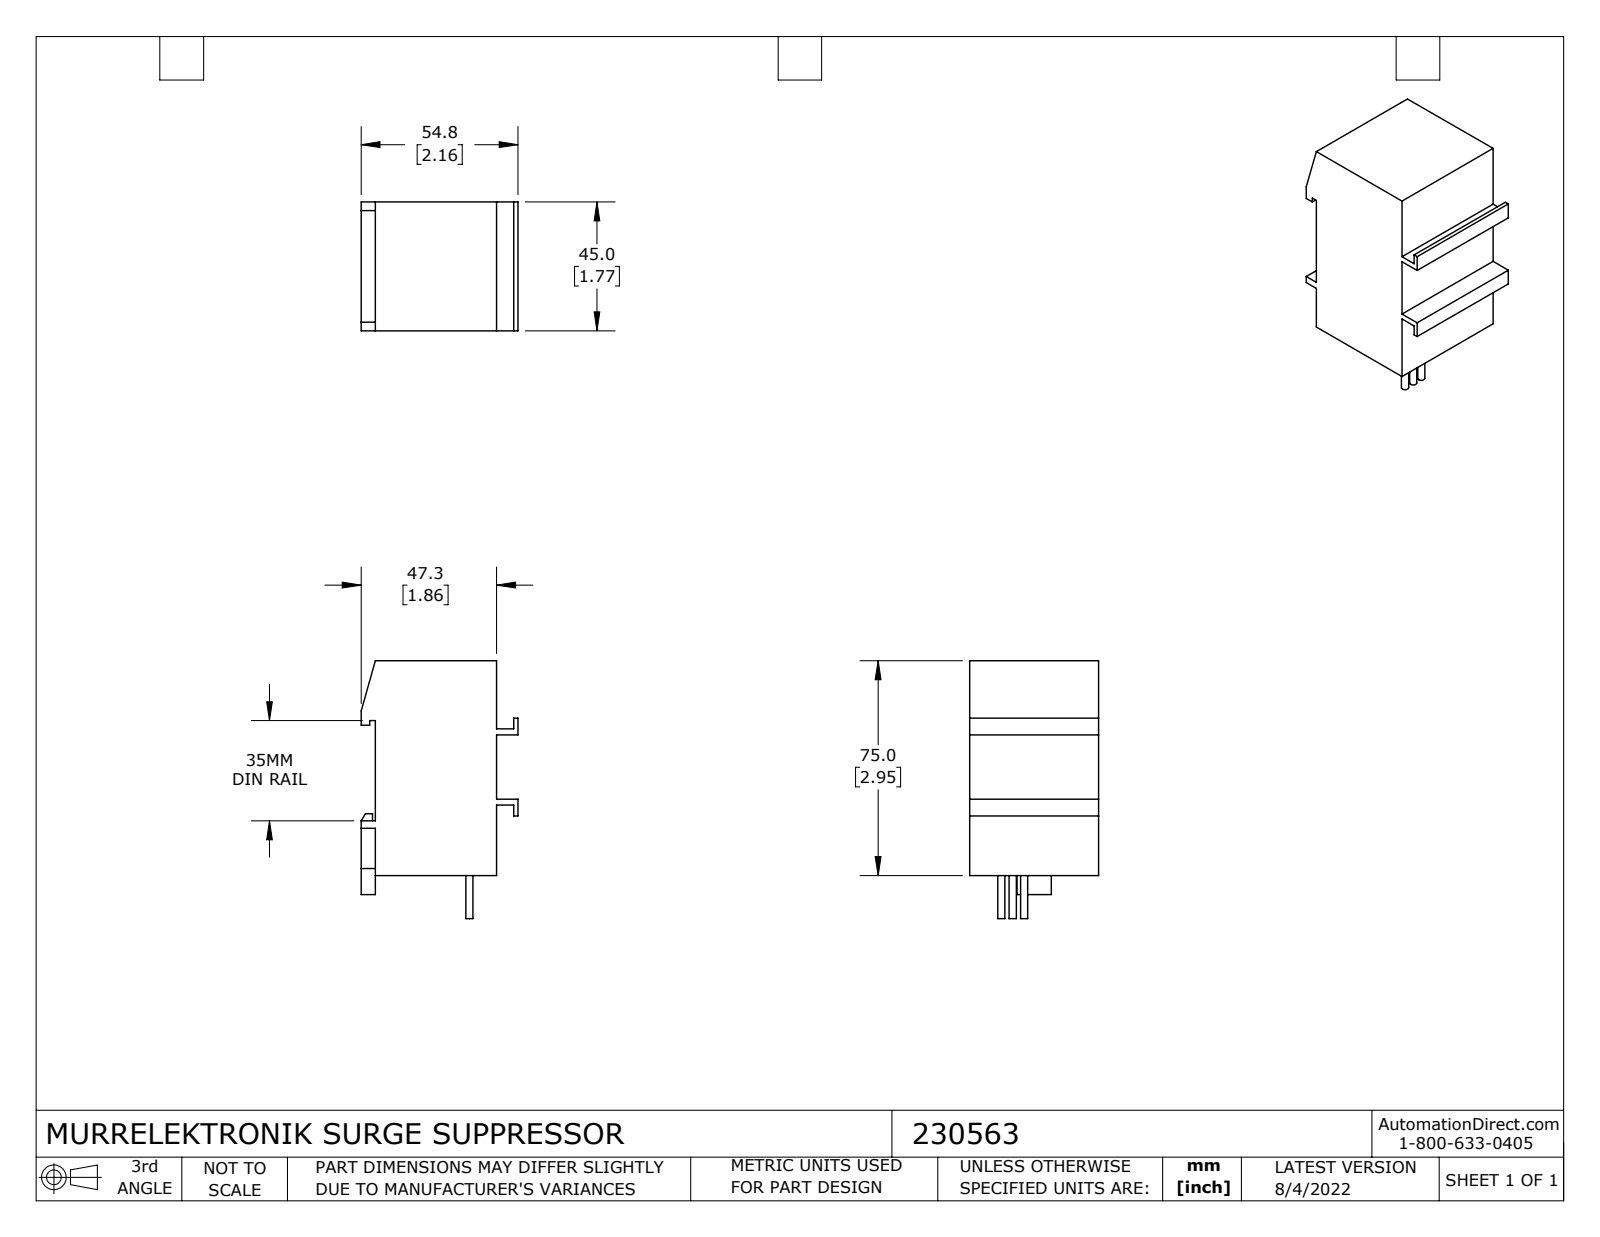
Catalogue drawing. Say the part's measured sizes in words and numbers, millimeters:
The part is named "230563". Its 3-D file was written by "SolidWorks 2021 (CONFIG_CONTROL_DESIGN)". It is 1 solid with 56 faces: 50 planar, 6 cylindrical and 0 other. Overall it measures 90 by 54.8 by 45 millimeters. Its volume is 148 926 cubic millimeters and its surface area 21 091 square millimeters. Round bosses or shafts: 3 of diameter 2.5. The main face-to-face distances are 45, 42.3, 75, 5, 47.3, 48.3, 2.1, 24.5, 7.5, 49.8.
